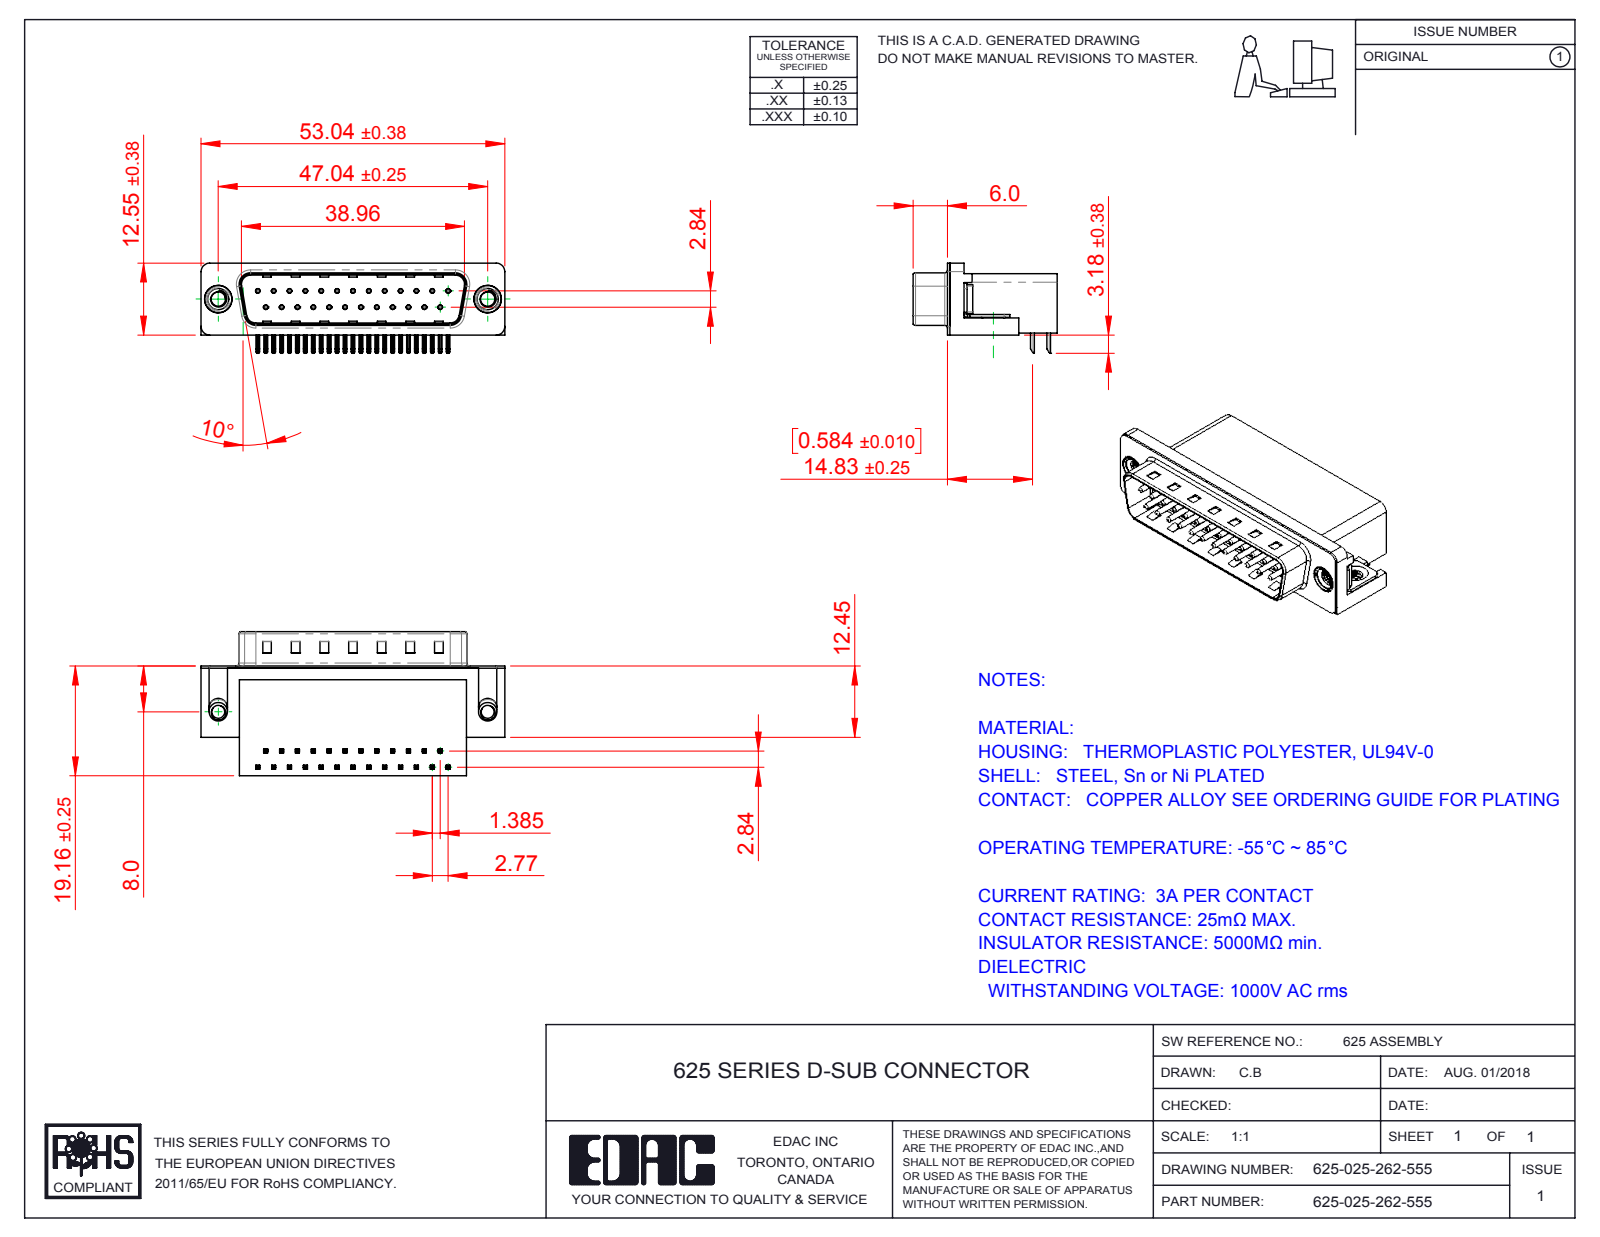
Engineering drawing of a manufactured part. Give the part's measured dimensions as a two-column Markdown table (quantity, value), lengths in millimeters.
| quantity | value |
| --- | --- |
| part name | 625 Contact Bottom; 625-025-262-555; 625 4-40 Threaded Board Mount; 625 Contact Top (+3 more) |
| STEP written by | SolidWorks 2016 (CONFIG_CONTROL_DESIGN) |
| units | millimeters |
| bodies | 31 solids, 2297 faces (1407 planar, 677 cylindrical, 213 other) |
| overall size | 53.04 × 25.16 × 15.73 |
| volume | 9 170 mm³ |
| surface area | 8 944 mm² |
| round holes (diameter × count) | 0.35 × 25, 0.8 × 25, 2.26 × 2, 2.5 × 2, 4 × 2, 4.8 × 2, 5 × 2 |
| round bosses / shafts (diameter × count) | 0.75 × 25, 4.9 × 2, 4.75 × 2, 3.9 × 2, 3.26 × 2 |
| partial cylindrical surfaces (radius × count) | 0.25 × 108, 0.12 × 50, 1 × 16, 0.5 × 9, 1.6 × 8, 1.5 × 7, 0.9 × 4, 2 × 4 |
| main face-to-face distances | 0.4, 10.35, 18.76, 2.1, 8.76, 10.46, 10.86, 1.7, 19.16, 10.11 |
| hole center spacings | 3.16, 2.77, 11.08, 5.54, 8.31, 5.03, 13.85, 7.48 |
